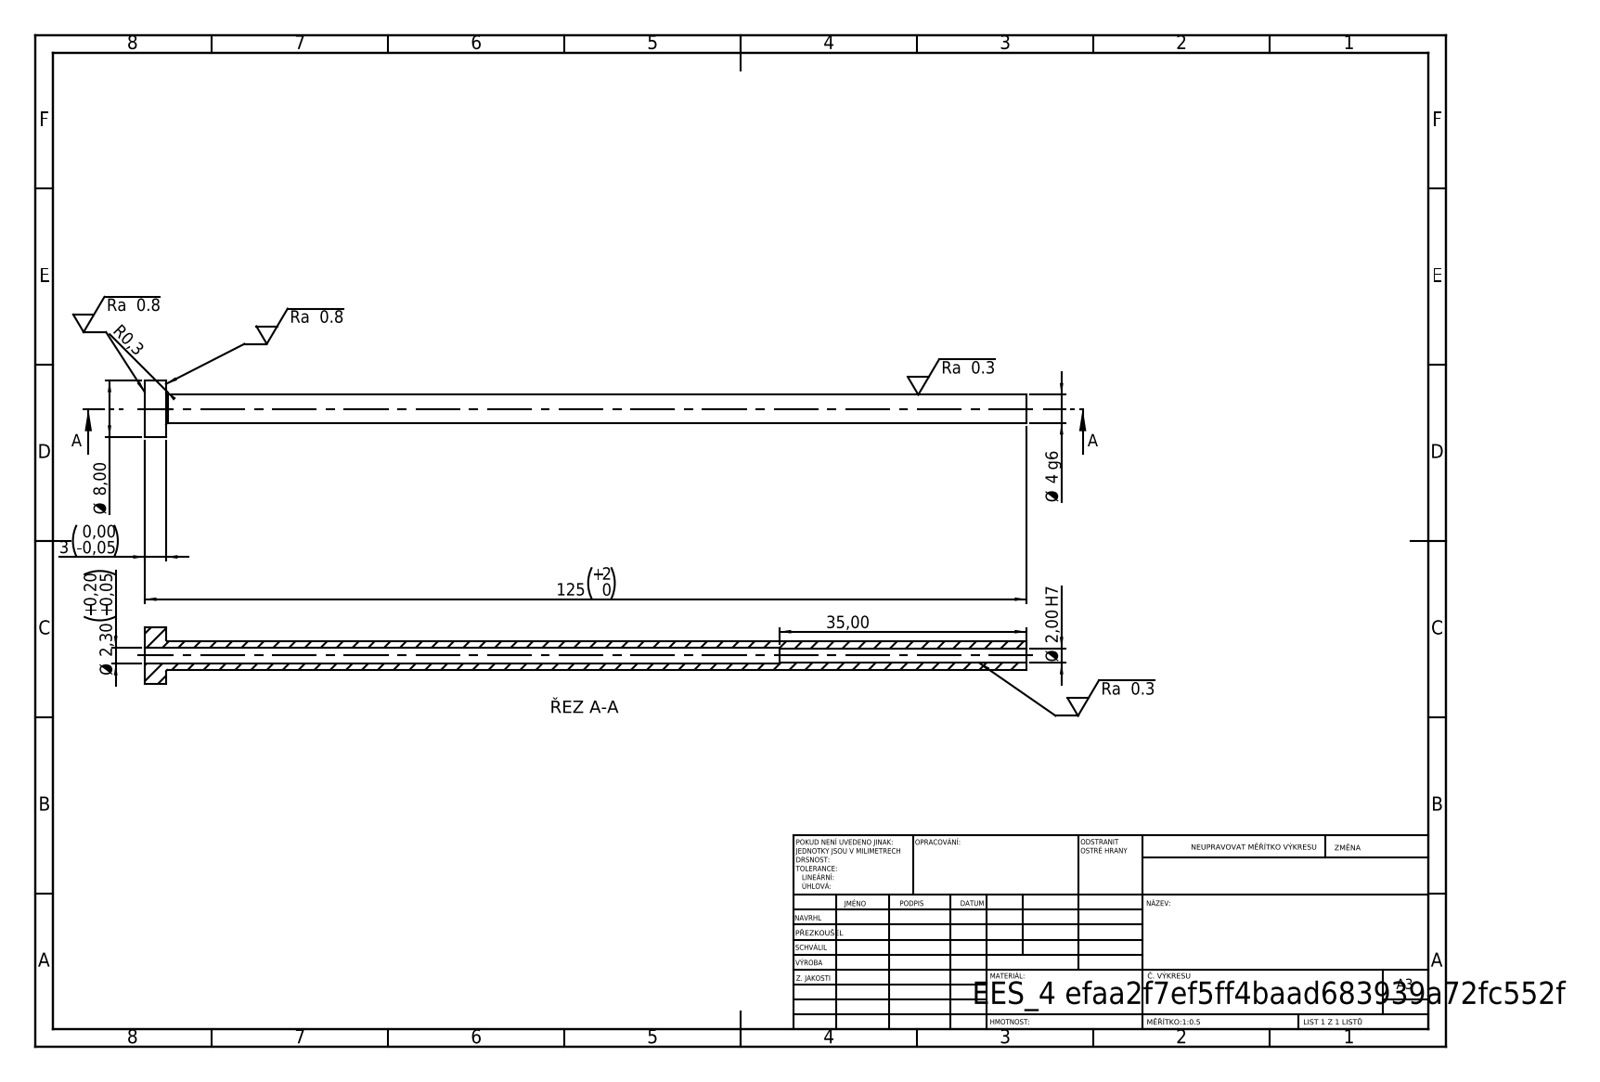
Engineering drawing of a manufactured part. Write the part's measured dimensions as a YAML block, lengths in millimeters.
step_written_by: "SolidWorks 2019 (CONFIG_CONTROL_DESIGN)"
units: millimeters
bodies: {solids: 1, faces: 14, planar: 4, cylindrical: 8, other: 2}
overall_size: [125, 8, 8]
volume: 1200
surface_area: 2571
round_holes:
  - {diameter: 2, count: 1}
  - {diameter: 2.3, count: 1}
round_bosses_or_shafts:
  - {diameter: 8, count: 1}
  - {diameter: 4, count: 1}
face_to_face_distances: [3, 125, 122, 90, 87, 35]
